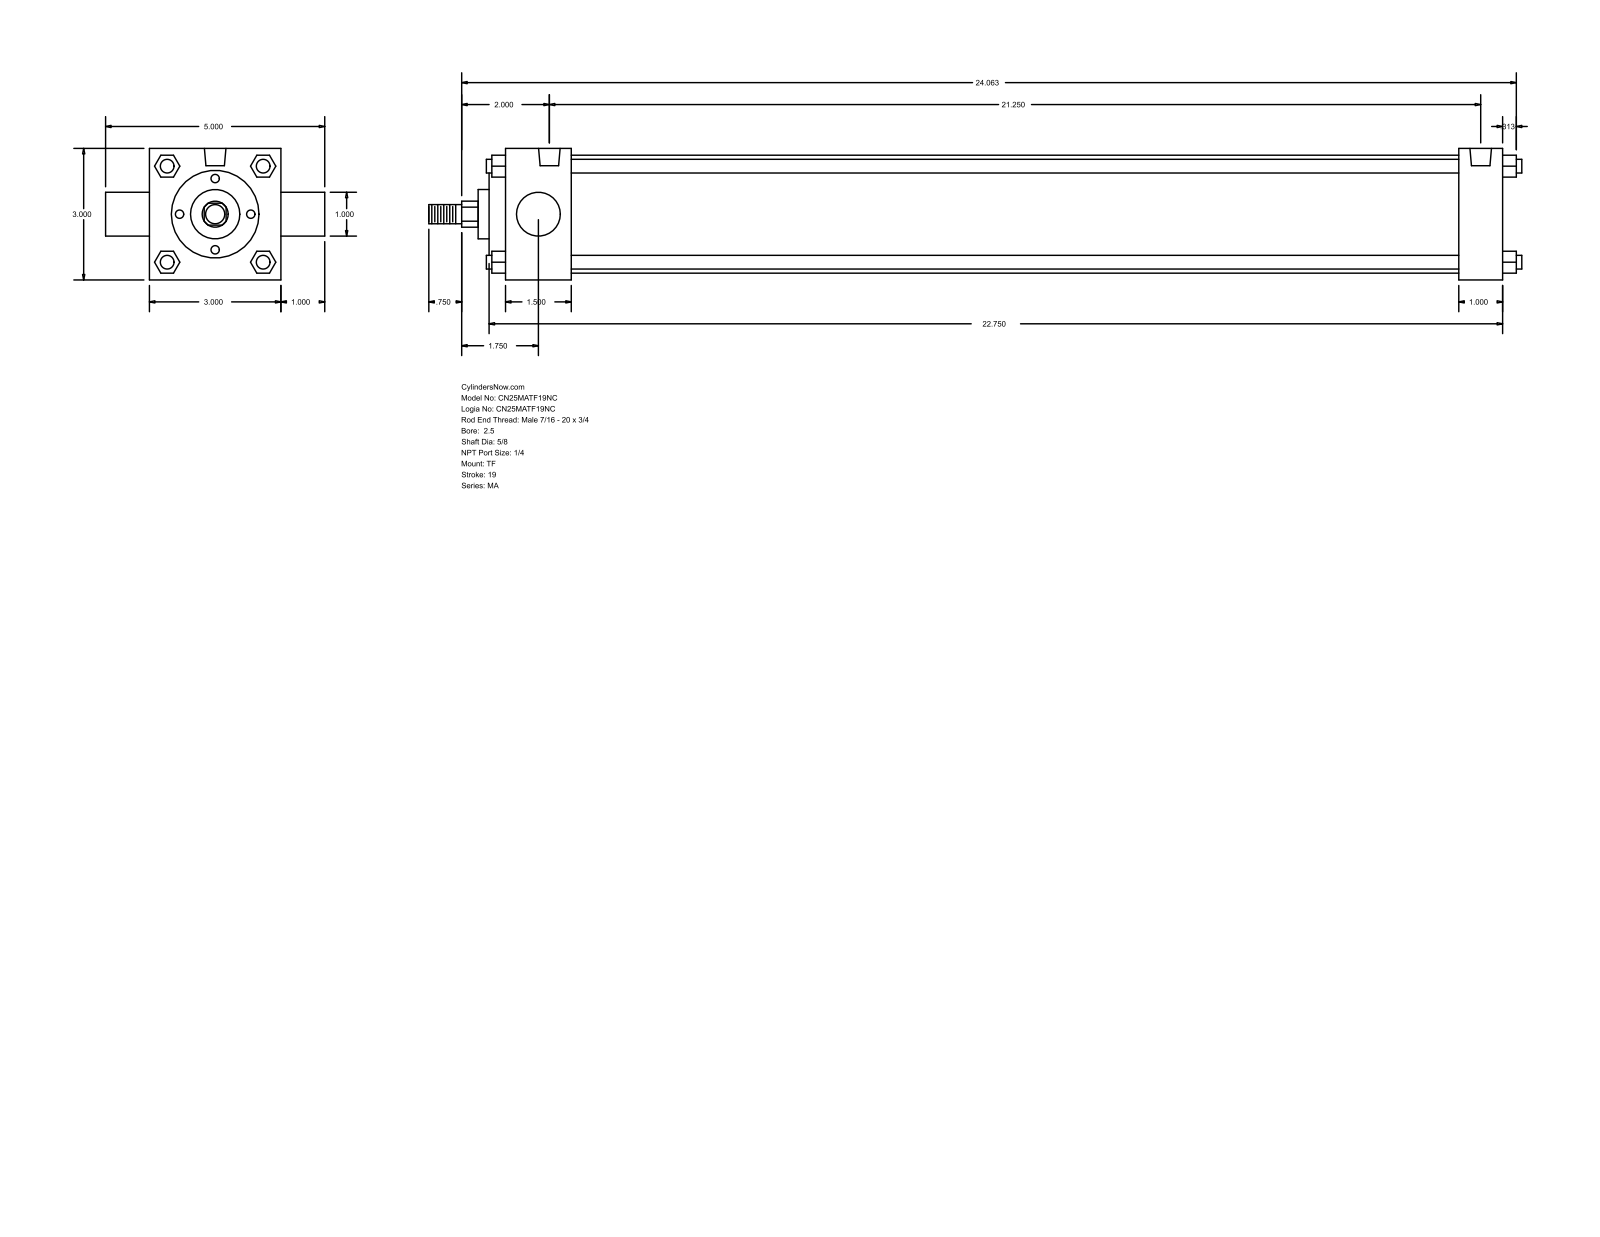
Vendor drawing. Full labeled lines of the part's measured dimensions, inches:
Part name (STEP PRODUCT): MA_TF__0250_0.625
STEP written by: GSSL Pune (CONFIG_CONTROL_DESIGN)
Units: inches
Bodies: 0 solids, 122 faces (93 planar, 29 cylindrical, 0 other)
Overall size (bounding box): 24.937 × 5 × 3
Round holes (diameter × count): ⌀0.313 ×3, ⌀0.492 ×2
Round bosses / shafts (diameter × count): ⌀0.313 ×4, ⌀2.69 ×1, ⌀2 ×1, ⌀1.125 ×1, ⌀1 ×1, ⌀0.625 ×1, ⌀0.437 ×1
Partial cylindrical surfaces — rounded edges, fillets, slot ends (radius × count): R0.297 ×1
Main face-to-face distances: 3, 22.75, 1, 1.5, 21.75, 20.25, 21.25, 0.5, 0.375, 1.875
Hole centre spacings: 21.25
